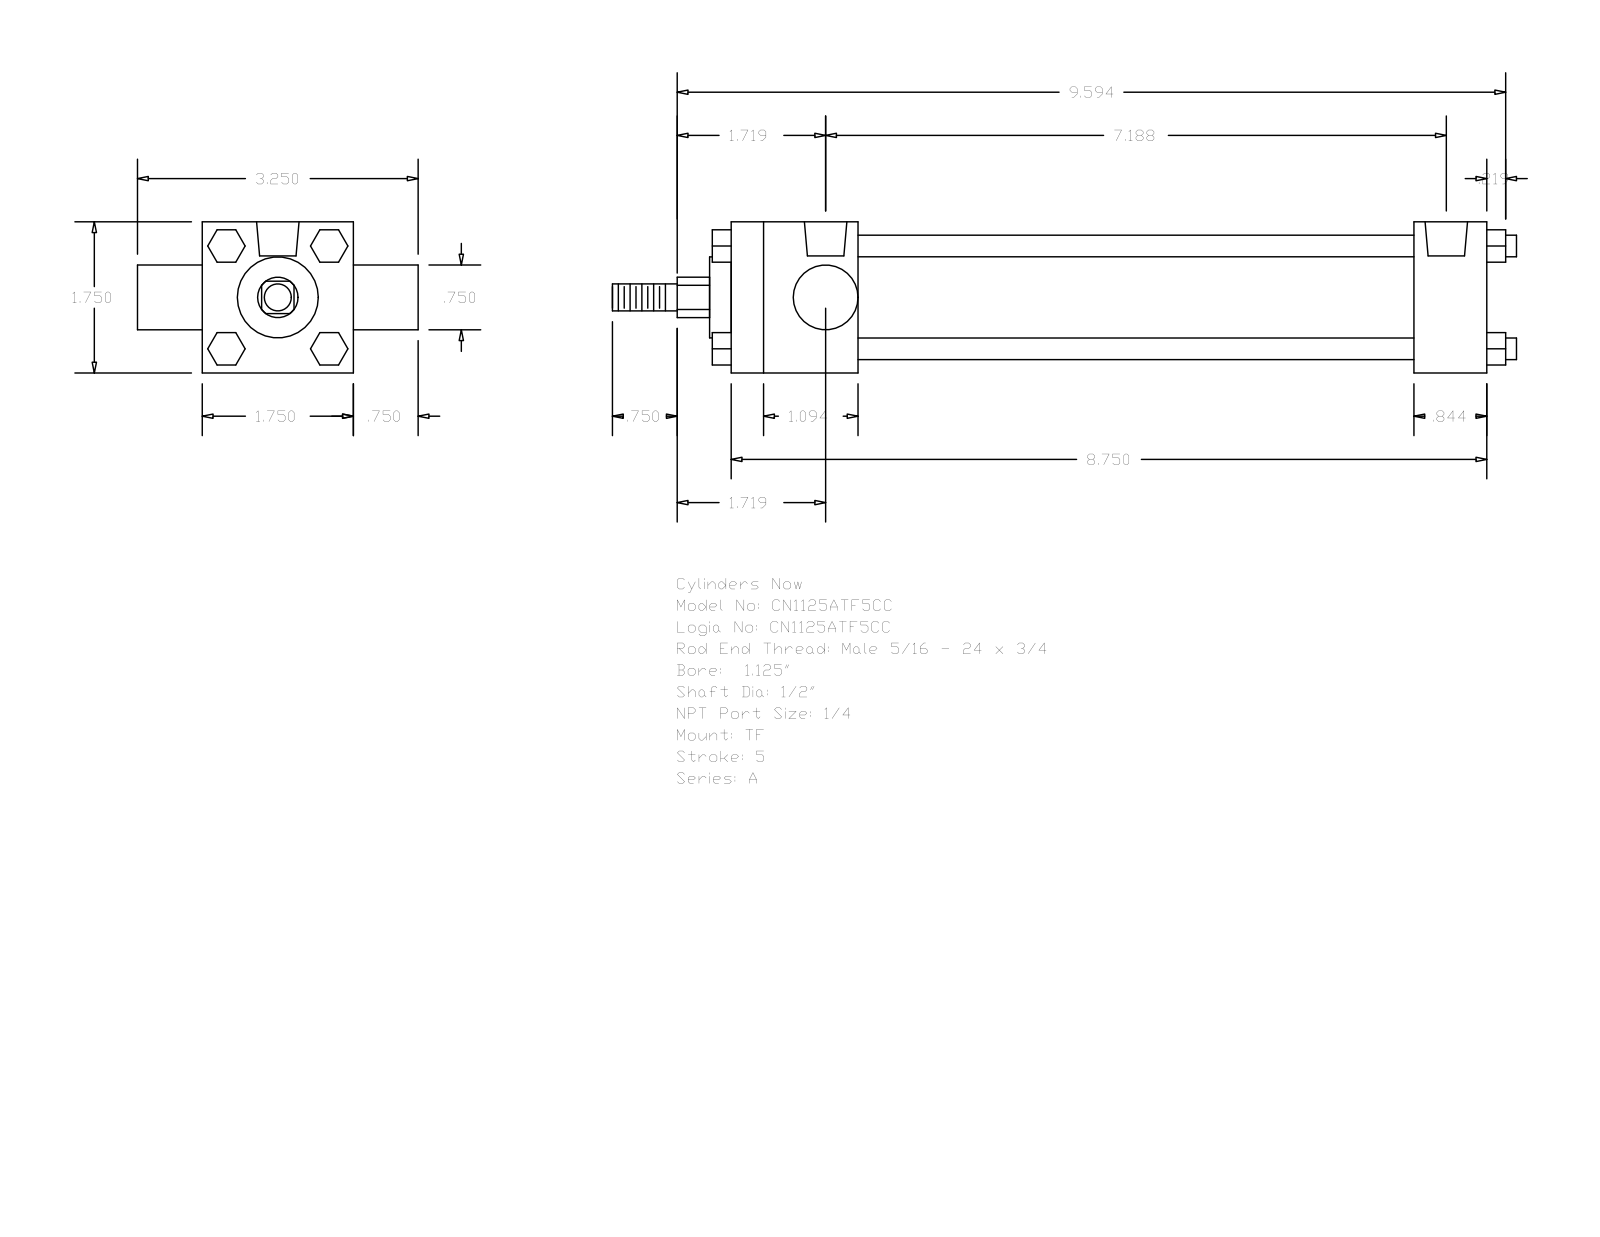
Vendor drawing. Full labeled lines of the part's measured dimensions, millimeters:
Part name (STEP PRODUCT): A_TF__0112_0.5
STEP written by: GSSL Pune (CONFIG_CONTROL_DESIGN)
Units: millimetres
Bodies: 0 solids, 120 faces (92 planar, 28 cylindrical, 0 other)
Overall size (bounding box): 265.91 × 82.55 × 44.45
Round holes (diameter × count): ⌀5.56 ×3, ⌀12.49 ×2
Round bosses / shafts (diameter × count): ⌀6.35 ×4, ⌀31.88 ×1, ⌀23.81 ×1, ⌀19.05 ×1, ⌀12.7 ×1, ⌀7.94 ×1
Partial cylindrical surfaces — rounded edges, fillets, slot ends (radius × count): R5.94 ×1
Main face-to-face distances: 44.46, 222.24, 200.81, 21.43, 37.3, 163.51, 184.94, 19.04, 63.5, 9.53
Hole centre spacings: 1.58, 1.59, 179.39, 180.97, 180.98, 182.56
